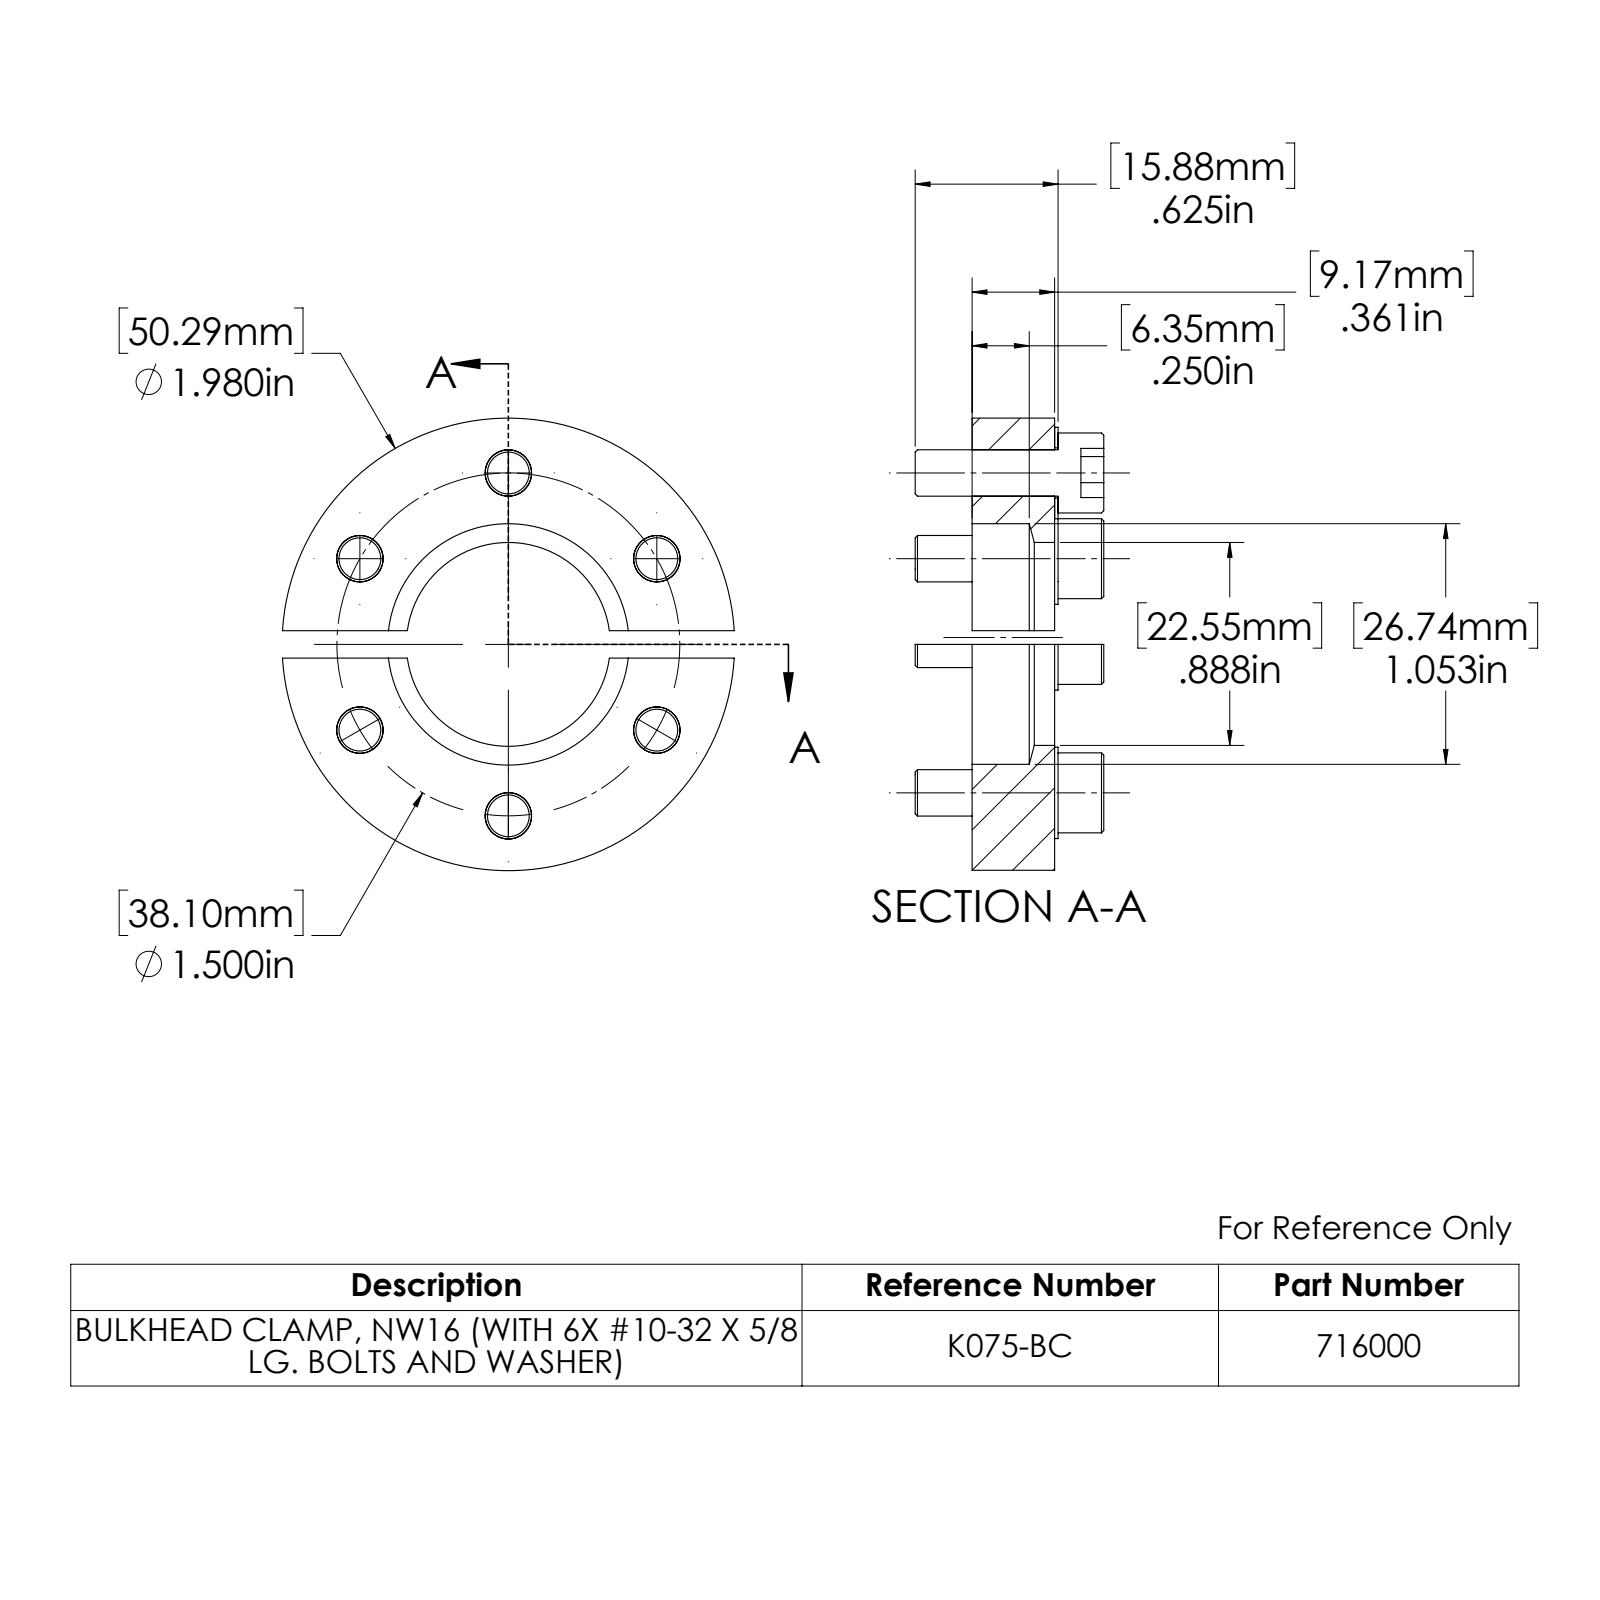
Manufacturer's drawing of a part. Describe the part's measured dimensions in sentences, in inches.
The part is named "716000". Its 3-D file was written by "SolidWorks 2022 (AUTOMOTIVE_DESIGN)". It is 8 solids with 140 faces: 68 planar, 45 cylindrical and 27 other. Overall it measures 1.98 by 1.976 by 0.911 inches. Its volume is 0.94 cubic inches and its surface area 15.05 square inches. Round holes: 6 of diameter 0.203, 1 of diameter 0.892, 1 of diameter 1.056. Round bosses or shafts: 6 of diameter 0.35, 6 of diameter 0.203, 1 of diameter 1.98. The main face-to-face distances are 0.361, 0.2, 0.1, 0.12, 0.561, 0.461, 0.35, 0.711, 0.811, 0.911. The hole center spacings are 0.75, 1.299, 1.5, 1.299, 0.75, 0.75.
